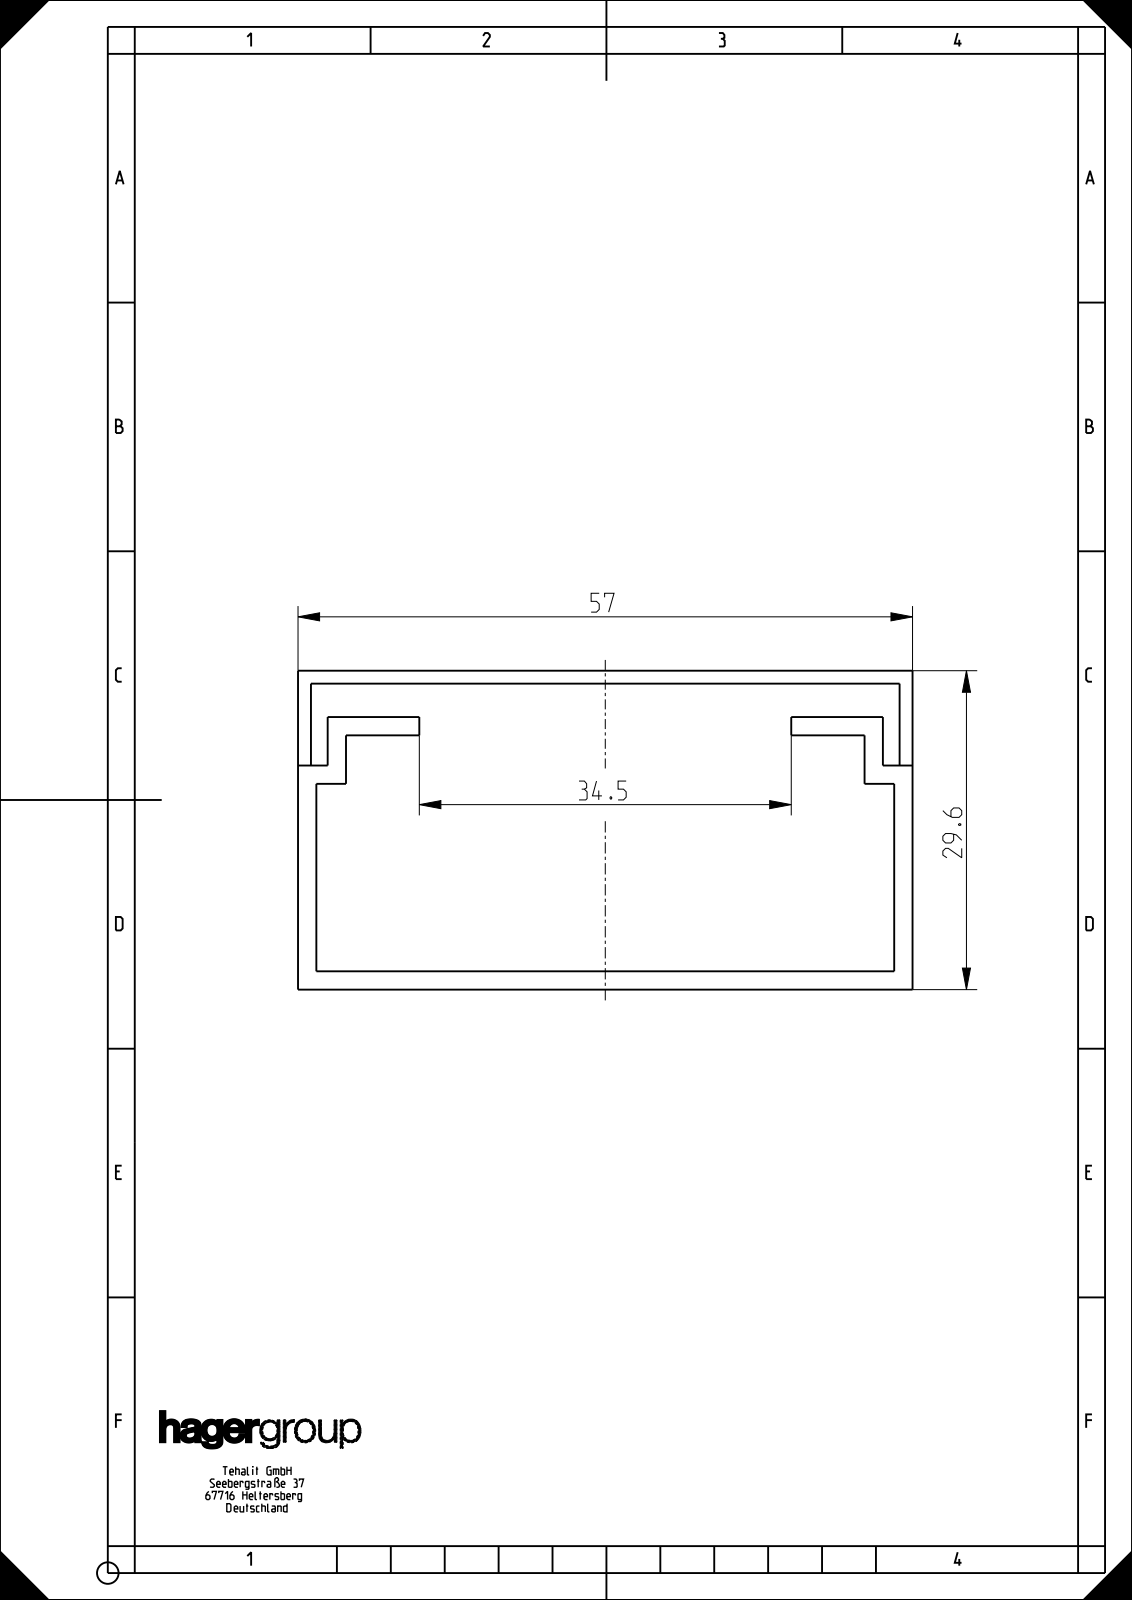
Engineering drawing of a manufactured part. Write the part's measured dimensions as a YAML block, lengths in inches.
part_name: "LF300600KUN; LF300600KUN_D; LF300600KUN_ASM"
step_written_by: "CREO PARAMETRIC BY PTC INC, 2022162 (AUTOMOTIVE_DESIGN)"
units: inches
bodies: {solids: 2, faces: 192, planar: 96, cylindrical: 96, other: 0}
overall_size: [78.74, 2.244, 1.165]
volume: 36.01
surface_area: 1229
round_holes:
  - {diameter: 0.256, count: 16}
partial_cylinders:
  - {radius: 0.089, count: 32}
  - {radius: 0.128, count: 16}
face_to_face_distances: [0.067, 0.047, 1.165, 1.118, 1.051, 1.098, 2.177, 0.929, 2.244, 0.108]
hole_center_spacings: [5.043, 9.843, 14.805, 19.685, 24.631, 29.528, 34.467, 39.37]
